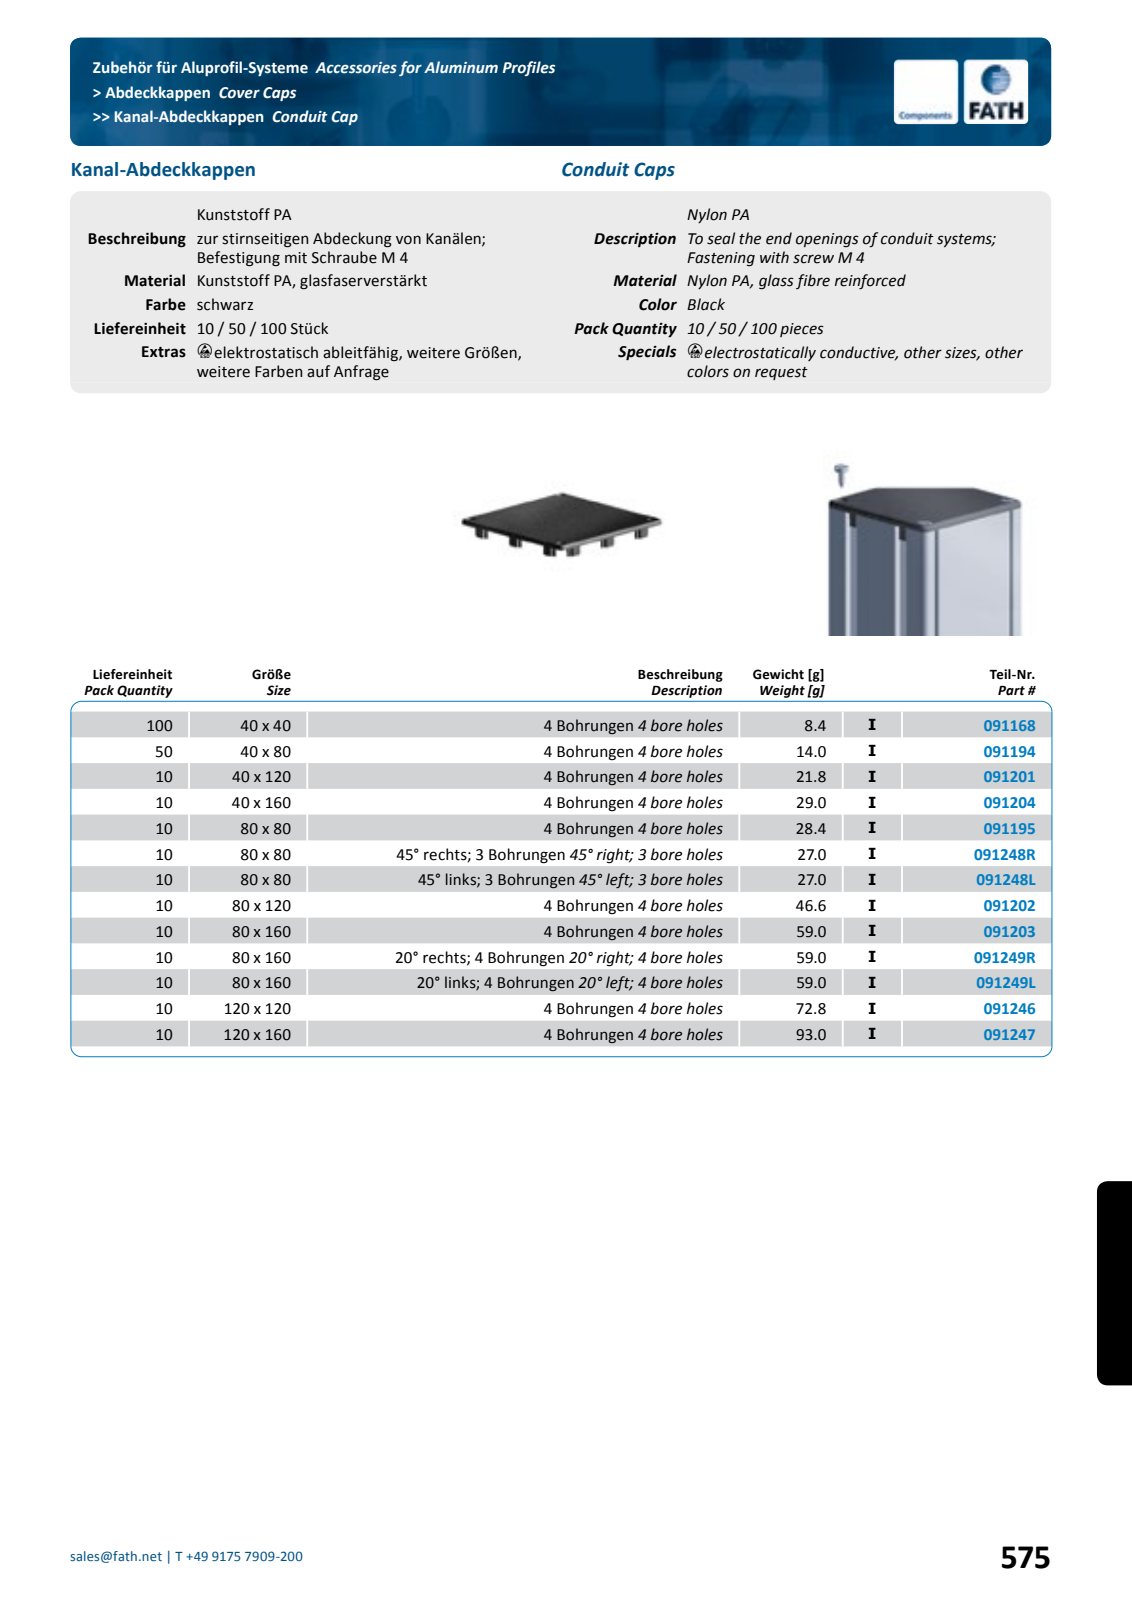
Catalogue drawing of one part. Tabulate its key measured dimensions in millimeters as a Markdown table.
| quantity | value |
| --- | --- |
| part name | fath_091195 |
| STEP written by | Spatial InterOp 3D (automotive_design) |
| units | millimeters |
| bodies | 1 solid, 331 faces (91 planar, 156 cylindrical, 84 other) |
| overall size | 80 × 80 × 13 |
| volume | 21 400 mm³ |
| surface area | 16 069 mm² |
| round holes (diameter × count) | 4.5 × 4, 8.2 × 4 |
| round bosses / shafts (diameter × count) | 7.5 × 4 |
| partial cylindrical surfaces (radius × count) | 0.2 × 84, 2.5 × 4, 3 × 4 |
| main face-to-face distances | 3, 1, 4, 2, 6.8, 73.2, 13, 3.8, 70.2, 77 |
| hole center spacings | 66.2, 66.4, 93.76 |
